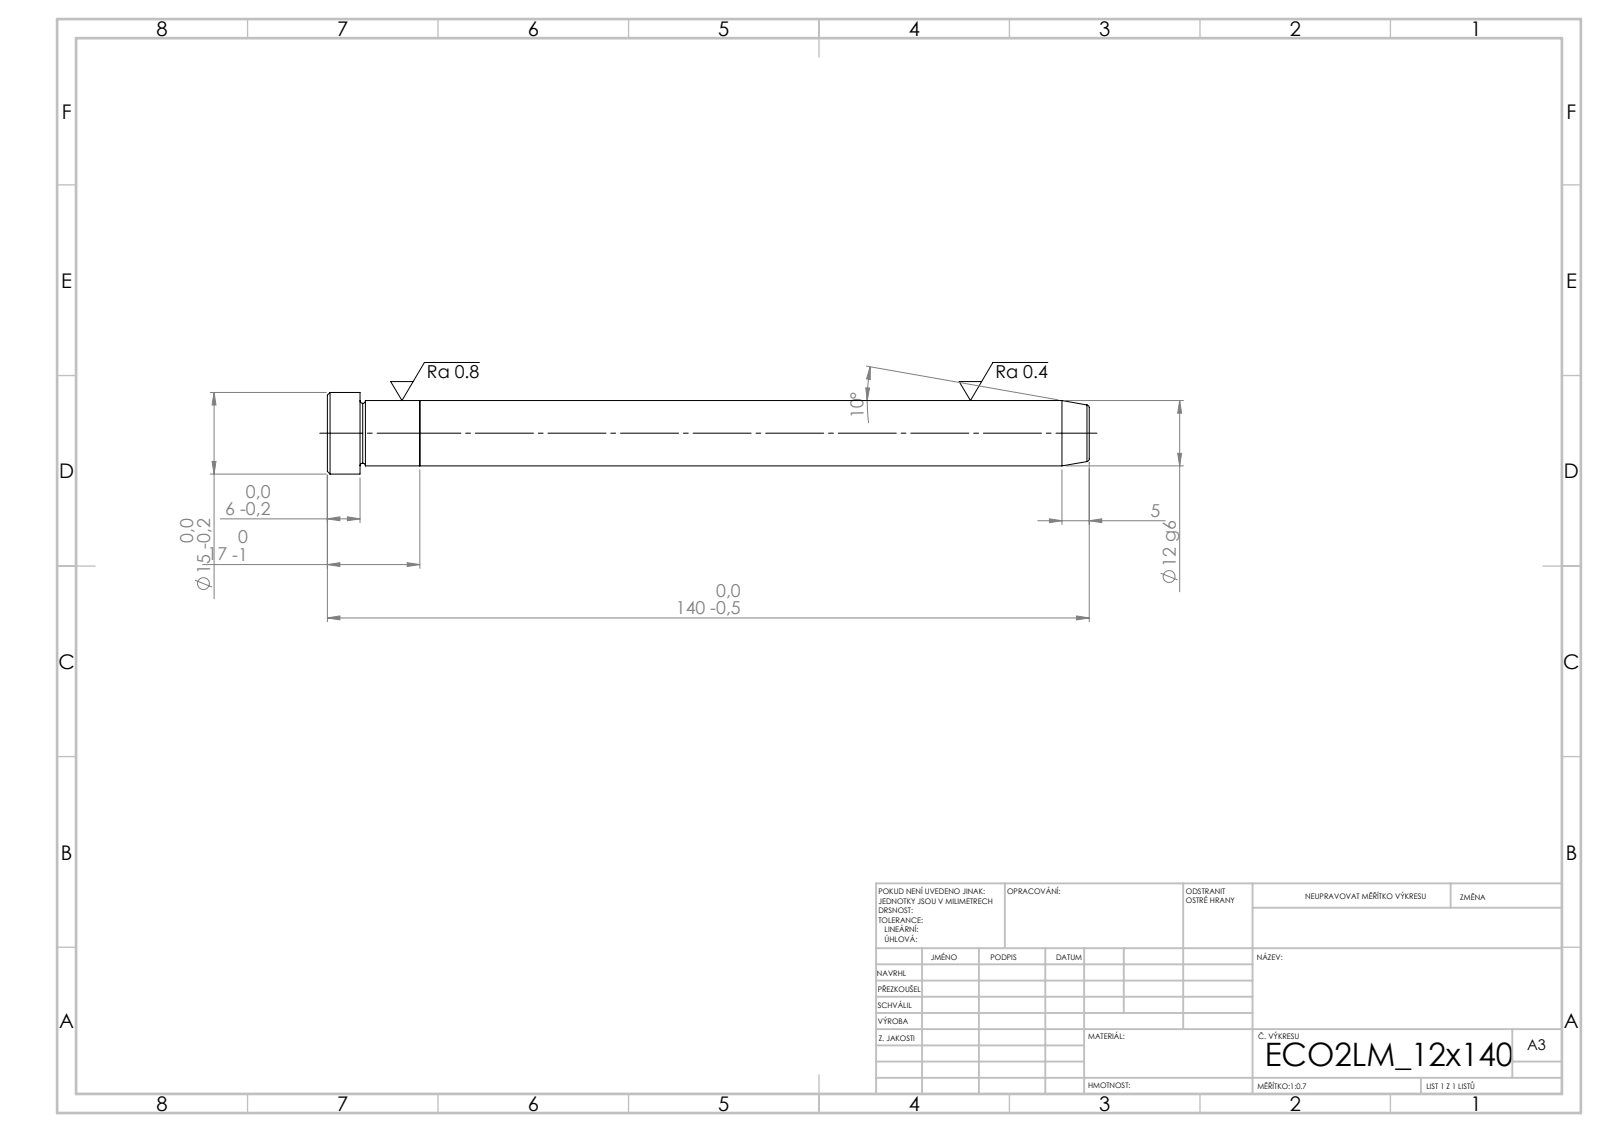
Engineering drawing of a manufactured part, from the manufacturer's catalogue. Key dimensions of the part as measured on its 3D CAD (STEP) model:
STEP written by: SolidWorks 2019 (CONFIG_CONTROL_DESIGN)
Units: millimetres
Bodies: 2 solids, 21 faces (5 planar, 6 cylindrical, 10 other)
Overall size (bounding box): 140 × 15 × 15
Volume: 16 115 mm³ · Surface area: 5 872 mm²
Round bosses / shafts (diameter × count): ⌀15 ×1, ⌀12 ×1
Main face-to-face distances: 17, 123, 140, 134, 11, 6
